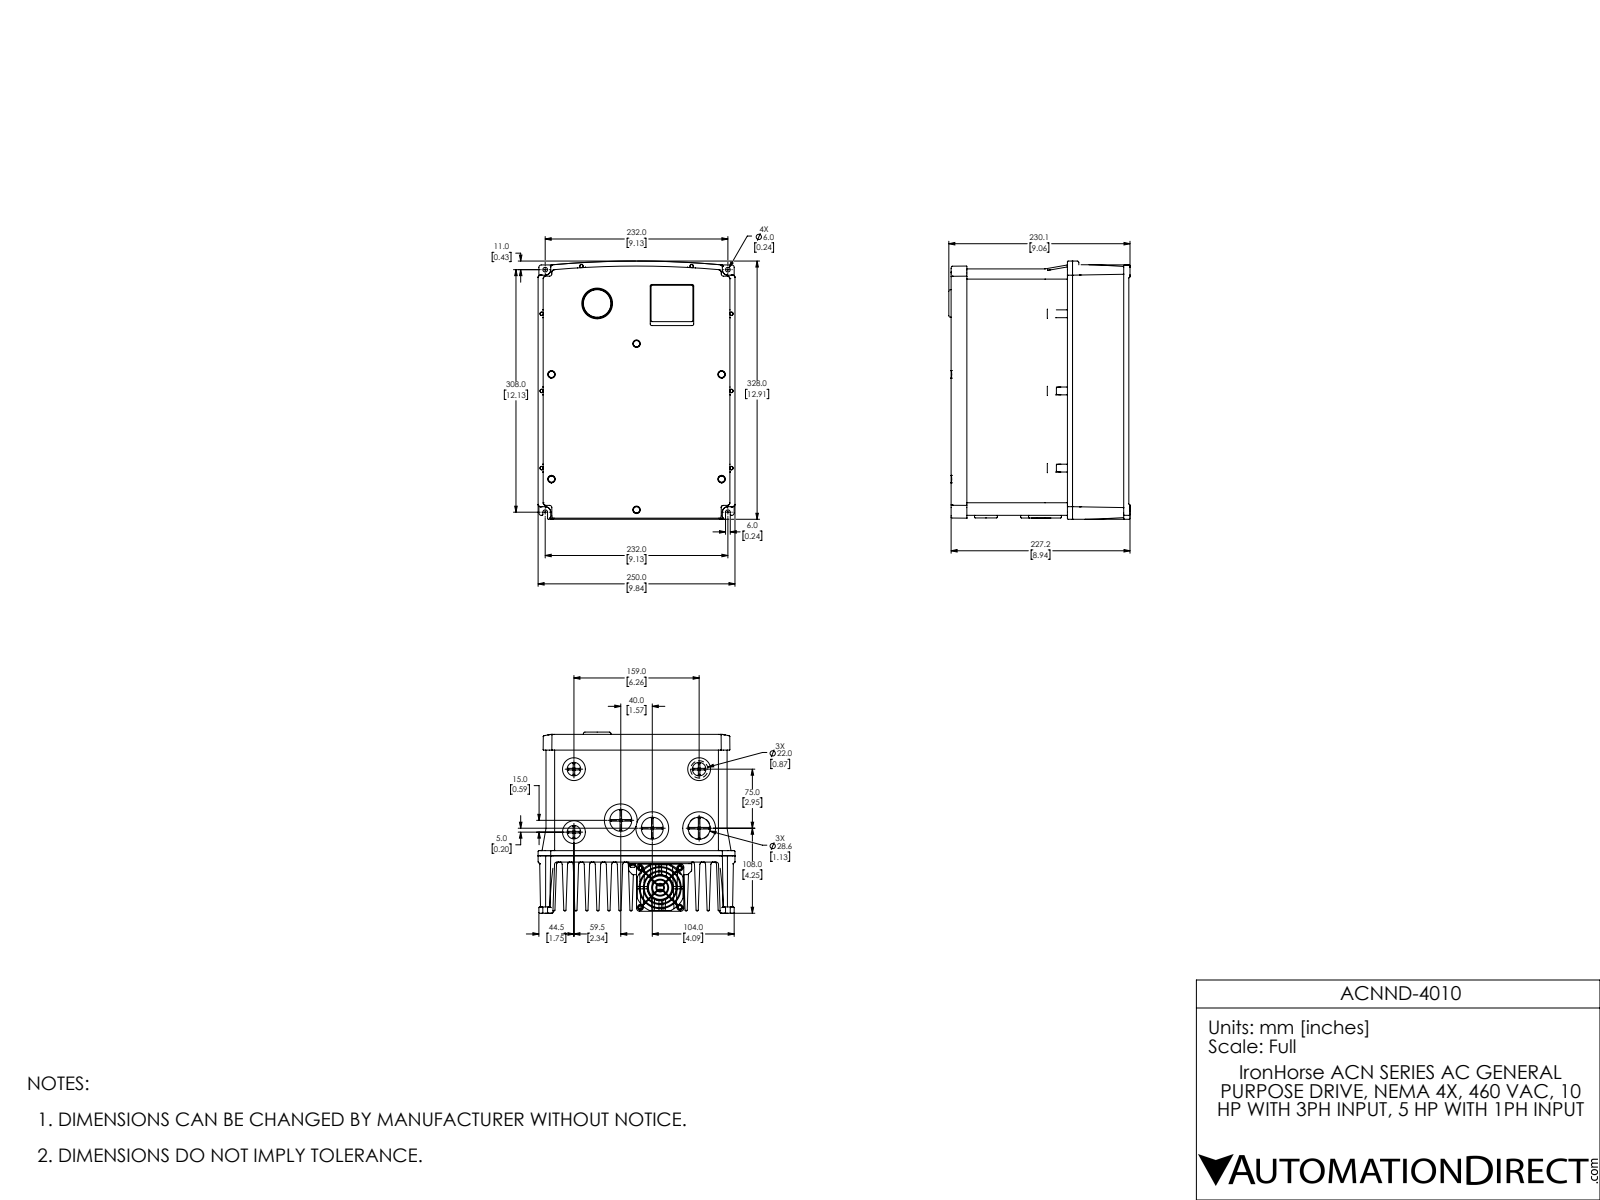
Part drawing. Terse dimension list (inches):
name: total_075_v2_assy_asm red surfs r1 red 3 combined from NON PDS 3F Ext Comb 1 w PLUGS No Knob cmb with NONPDS Knob 1
written by: SolidWorks 2017 (AUTOMOTIVE_DESIGN)
unit: in
bodies: 13 solids, 4225 faces (1220 planar, 1540 cylindrical, 1465 other)
size: 12.912 × 9.843 × 9.059
volume: 685.9 in³; area: 1 989 in²
holes: 43× ⌀0.157, 22× ⌀0.177, 8× ⌀0.28, 7× ⌀0.335, 3× ⌀0.677, 3× ⌀0.866, 3× ⌀1.024, 3× ⌀1.098, 3× ⌀1.524, 2× ⌀0.197, 2× ⌀0.236, 2× ⌀1.161
bosses: 14× ⌀0.315, 11× ⌀0.047, 8× ⌀0.354, 3× ⌀1.642, 3× ⌀1.35, 3× ⌀1.142, 3× ⌀0.85, 2× ⌀1.299
rounds: 228× R0.039, 169× R0.02, 104× R0.118, 71× R0.079, 28× R0.087, 28× R0.11, 17× R0.008, 16× R0.012
face distances: 1.101, 1.652, 2.753, 0.551, 2.202, 4.405, 3.854, 0.55, 3.304, 5.506
hole spacings: 1.392, 1.969, 3.182, 2.784, 9.628, 0.65, 1.148, 1.49
